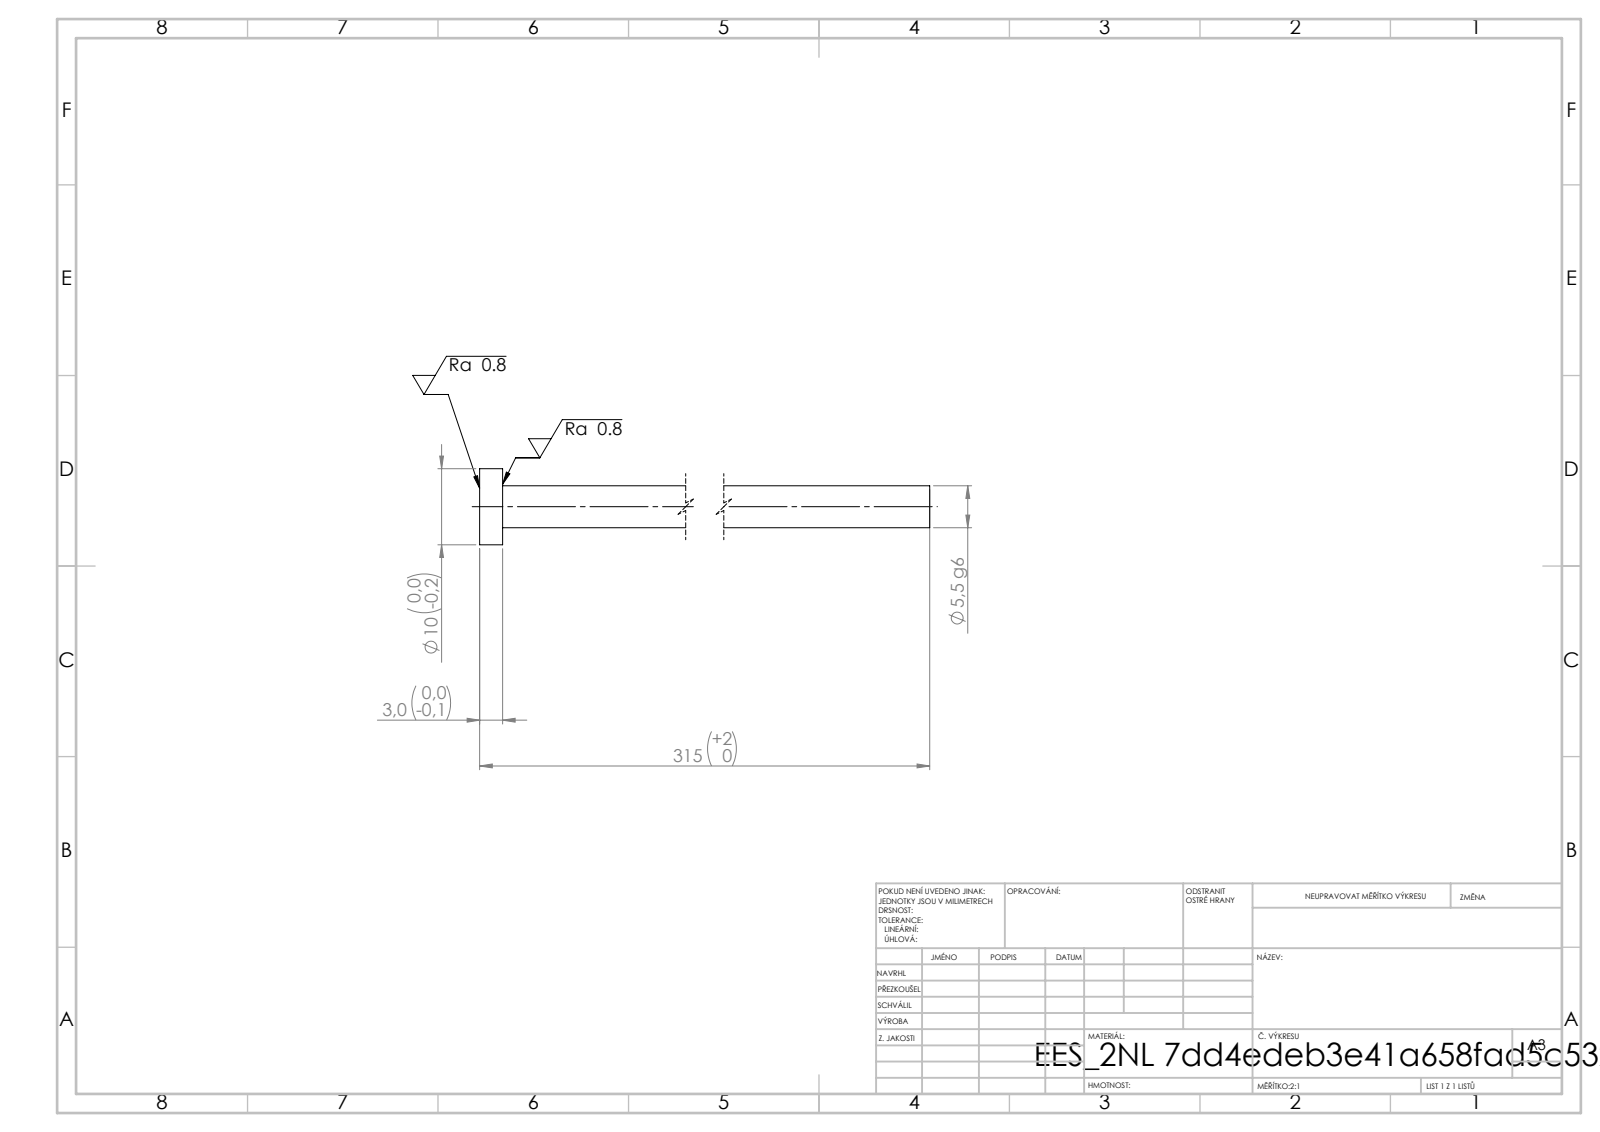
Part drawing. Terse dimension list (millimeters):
written by: SolidWorks 2019 (CONFIG_CONTROL_DESIGN)
unit: mm
bodies: 1 solid, 7 faces (3 planar, 4 cylindrical, 0 other)
size: 315 × 10 × 10
volume: 7 648 mm³; area: 5 642 mm²
bosses: 1× ⌀10, 1× ⌀5.5
face distances: 3, 315, 312
